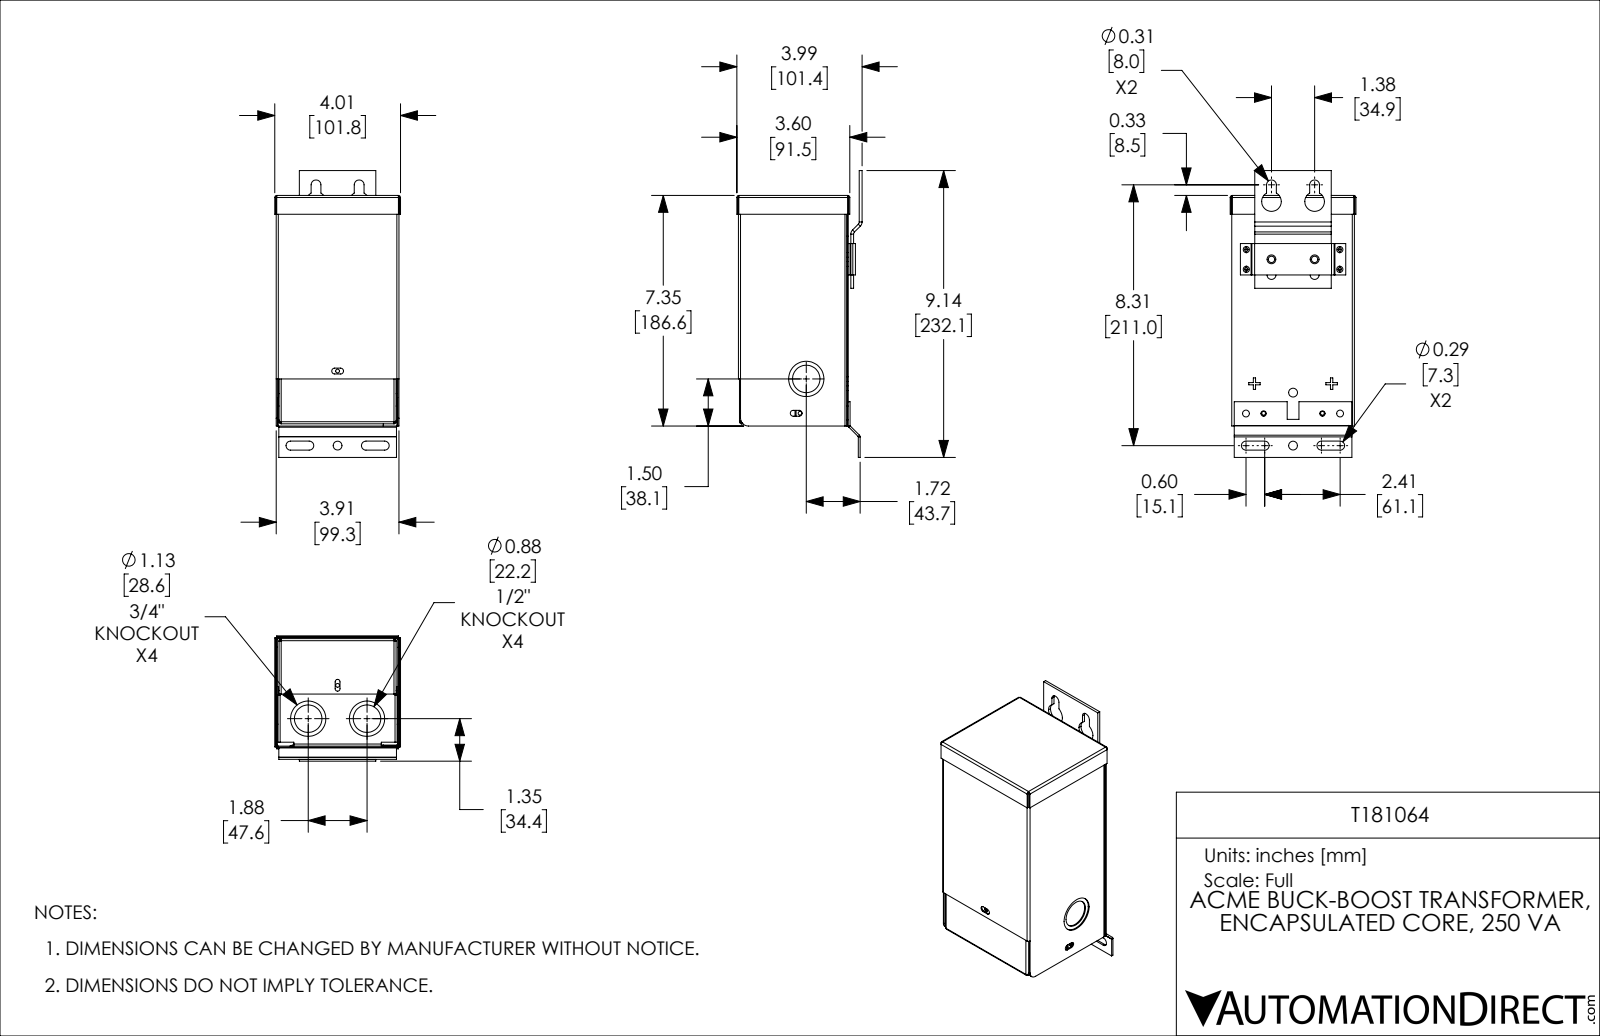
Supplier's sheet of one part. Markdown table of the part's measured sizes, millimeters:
| quantity | value |
| --- | --- |
| part name | T181064 |
| STEP written by | SolidWorks 2021 (CONFIG_CONTROL_DESIGN) |
| units | millimeters |
| bodies | 7 solids, 528 faces (326 planar, 154 cylindrical, 48 other) |
| overall size | 232.07 × 101.8 × 101.43 |
| volume | 113 073 mm³ |
| surface area | 227 401 mm² |
| round holes (diameter × count) | 3.05 × 5, 7.14 × 3, 7.14 × 3, 22.22 × 3, 28.57 × 3, 4.34 × 2, 4.76 × 2, 5.11 × 2, 5.54 × 2, 15.88 × 2, 28.58 × 1 |
| round bosses / shafts (diameter × count) | 30.4 × 3, 24.05 × 3 |
| partial cylindrical surfaces (radius × count) | 0.79 × 16, 1.7 × 16, 2.38 × 8, 0.66 × 4, 2.18 × 4, 3.66 × 4, 0.43 × 2, 1.96 × 2 |
| main face-to-face distances | 0.91, 87.99, 98.41, 87.08, 99.32, 97.5, 88.9, 1.53, 183.95, 182.42 |
| hole center spacings | 34.92, 12.7, 12.74, 14.27, 14.29, 29.09, 29.23, 34.94 |
